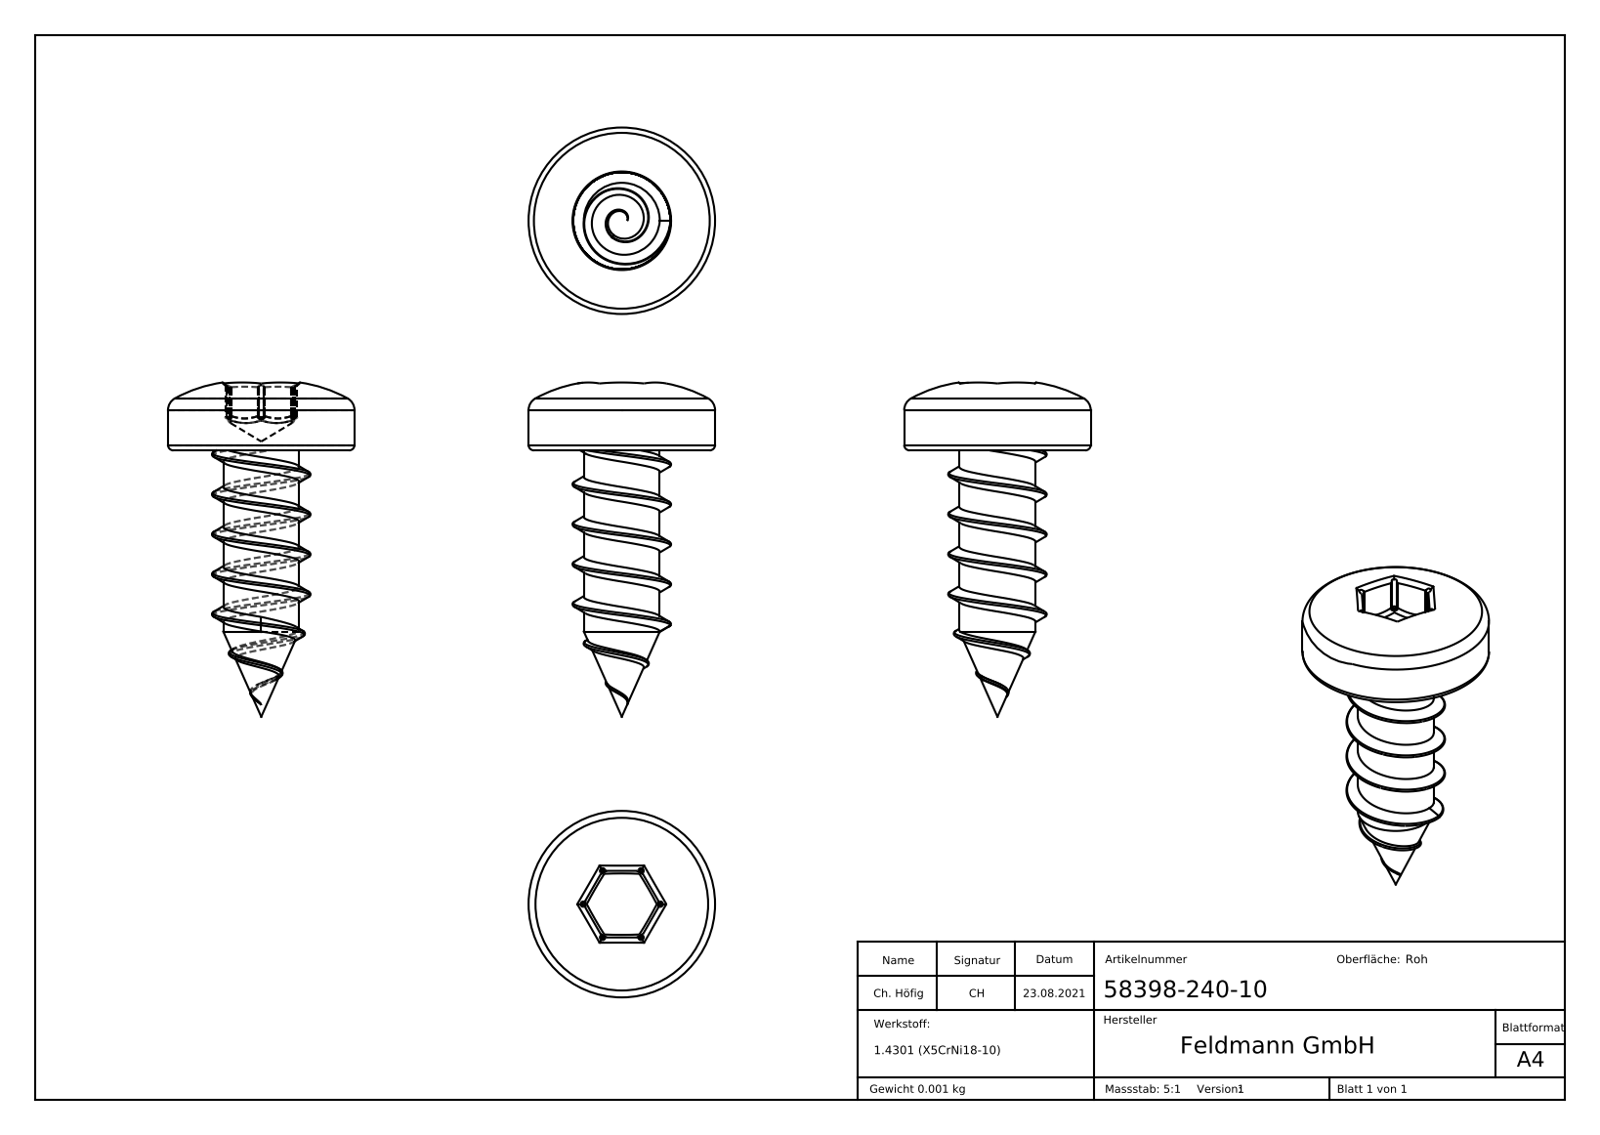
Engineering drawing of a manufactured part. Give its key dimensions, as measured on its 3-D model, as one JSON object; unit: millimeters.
{"part_name": "58398-240-10", "step_written_by": "SolidWorks 2018 (CONFIG_CONTROL_DESIGN)", "units": "millimeters", "bodies": {"solids": 1, "faces": 101, "planar": 13, "cylindrical": 20, "other": 68}, "overall_size": [12.17, 7, 7], "volume_mm3": 128, "surface_area_mm2": 223, "round_bosses_or_shafts": [[7, 1], [2.85, 1]], "partial_cylinders_radius": [[0.1, 6]], "face_to_face_distances": [2.5, 1.2]}
